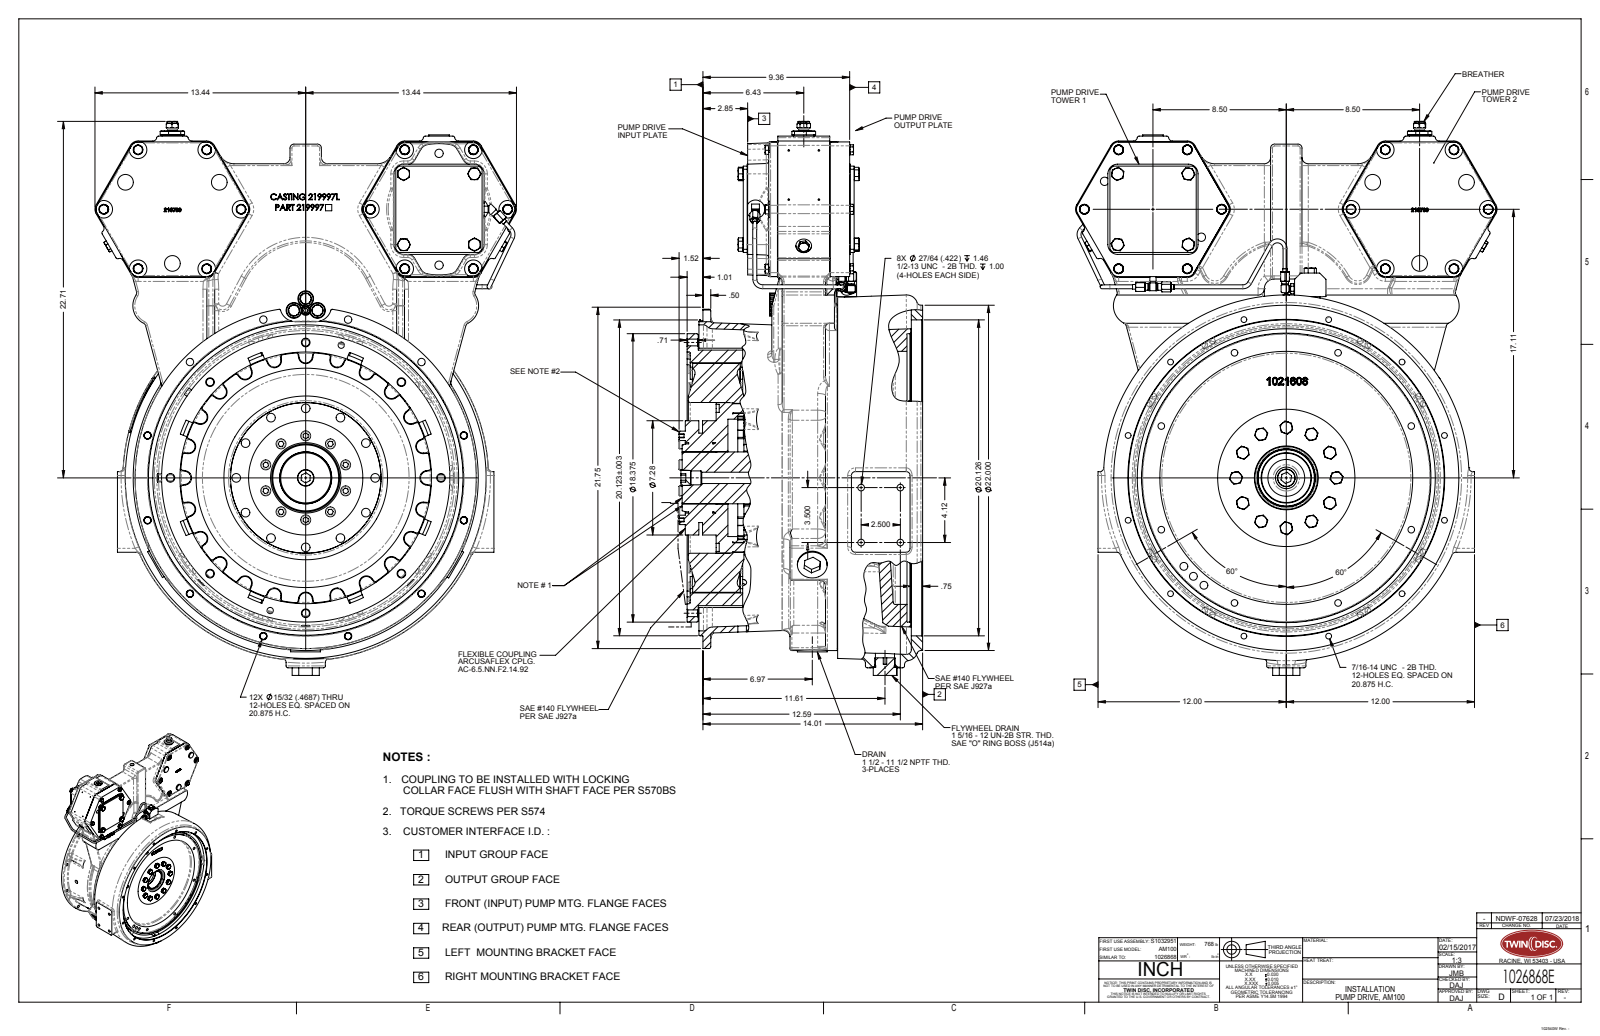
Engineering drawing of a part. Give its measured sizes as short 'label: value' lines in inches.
name: 1026868E
written by: SolidWorks 2015 (AUTOMOTIVE_DESIGN)
unit: in
bodies: 0 solids, 2927 faces (1074 planar, 884 cylindrical, 969 other)
size: 35.297 × 26.87 × 15.525
holes: 20× ⌀0.472, 12× ⌀0.368, 12× ⌀0.422, 10× ⌀0.437, 8× ⌀0.551, 4× ⌀0.578, 3× ⌀0.5, 2× ⌀0.107, 2× ⌀0.402, 2× ⌀0.531, 2× ⌀0.531, 2× ⌀0.625
bosses: 14× ⌀0.743, 14× ⌀0.62, 12× ⌀0.557, 10× ⌀0.63, 7× ⌀0.25, 4× ⌀1, 4× ⌀0.296, 3× ⌀0.93
rounds: 73× R0.12, 60× R0.25, 59× R0.5, 48× R0.1, 24× R0.42, 18× R0.459, 17× R0.56, 12× R0.06
face distances: 4.196, 3.539, 0.657, 0.584, 3.891, 8.589, 0.776, 2.763, 3.42, 0.5
hole spacings: 20.164, 10.437, 10.438, 18.078, 14.761, 20.875, 5.403, 14.761
